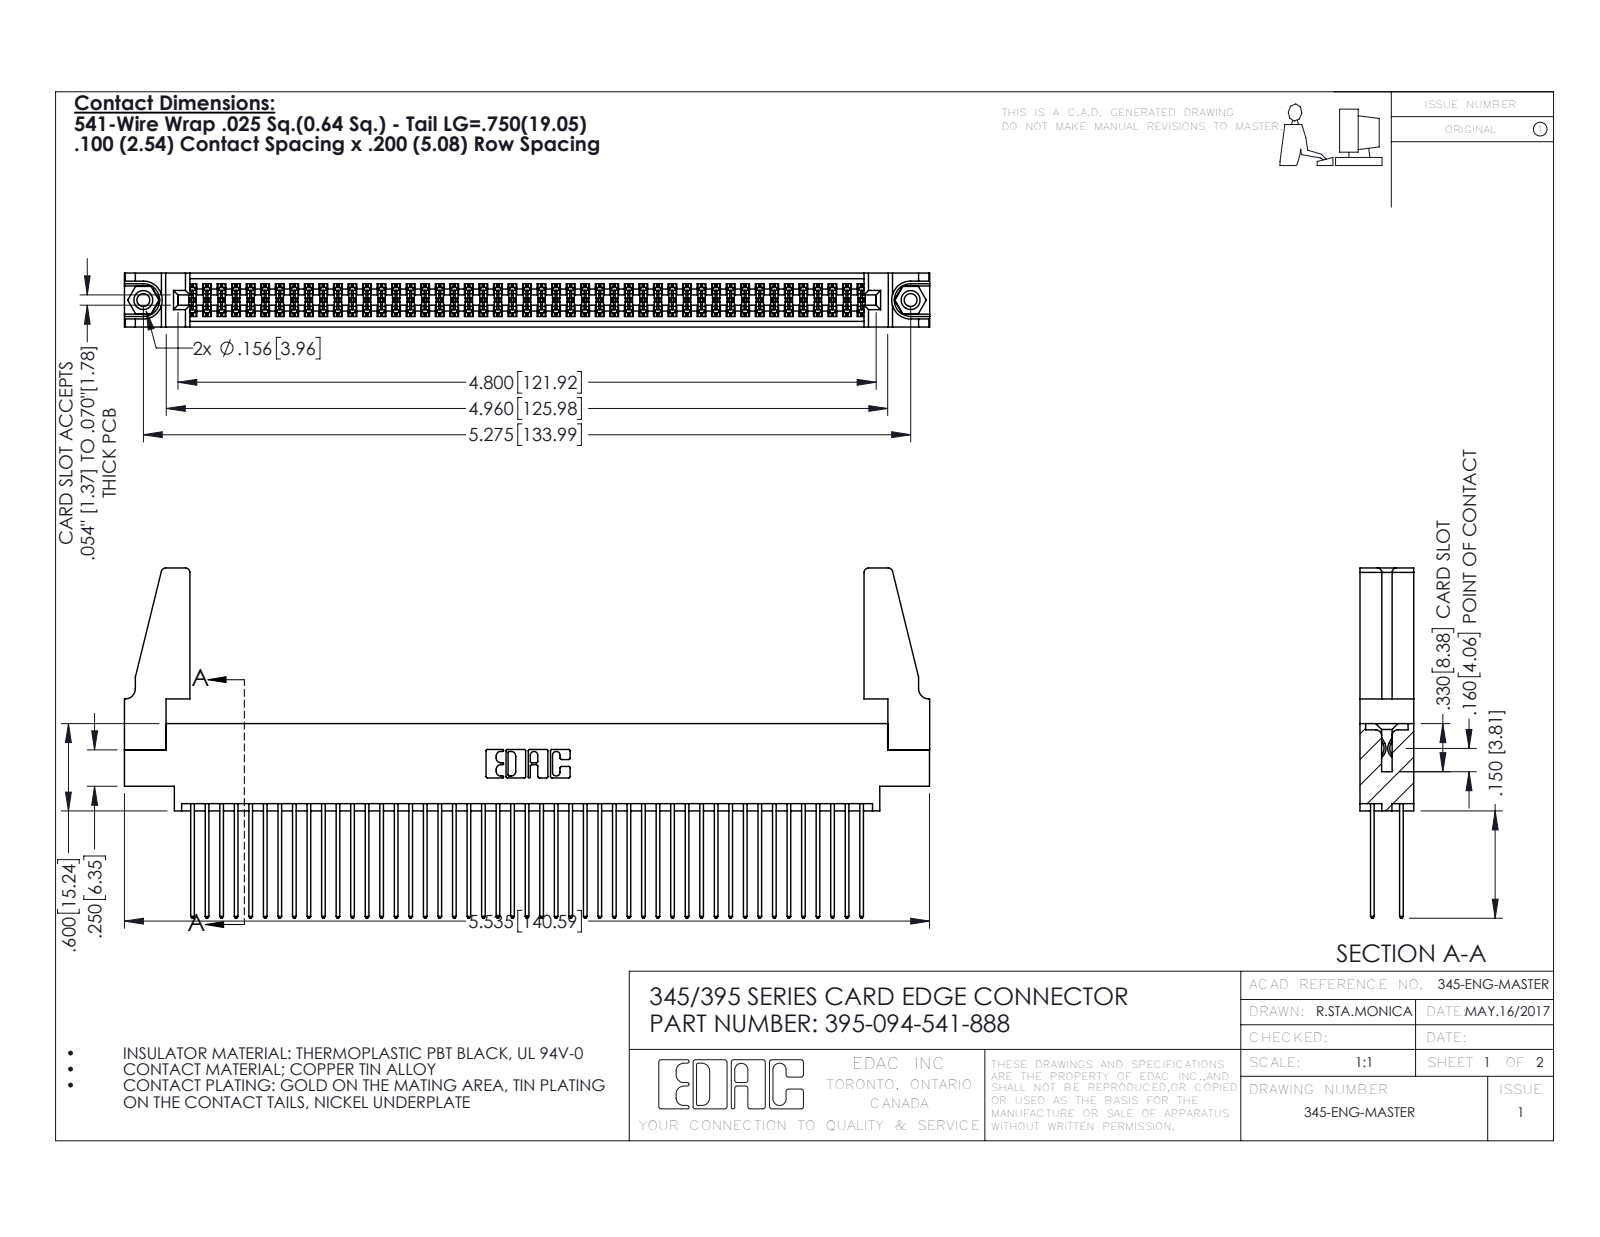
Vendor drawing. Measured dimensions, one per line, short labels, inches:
name: 345-292-001_345-293-141; 345-250-001_345-250-001-102; 345 Part_0.170 Offset - 0.156 Dia-TH; 345-220-078_345-220-088 (+1 more)
written by: SolidWorks 2016 (CONFIG_CONTROL_DESIGN)
unit: in
bodies: 99 solids, 4954 faces (3258 planar, 1680 cylindrical, 16 other)
size: 5.536 × 2.407 × 0.37
volume: 1.061 in³; area: 41.52 in²
holes: 2× ⌀0.089, 2× ⌀0.125, 2× ⌀0.156, 1× ⌀0.064
bosses: 2× ⌀0.155
rounds: 141× R0.006, 94× R0.01, 22× R0.01, 8× R0.03, 6× R0.007, 6× R0.031, 3× R0.026, 2× R0.014
face distances: 0.072, 0.298, 0.098, 0.272, 0.025, 0.2, 0.37, 0.225, 0.175, 0.149
hole spacings: 0.27, 5.039, 5.275
